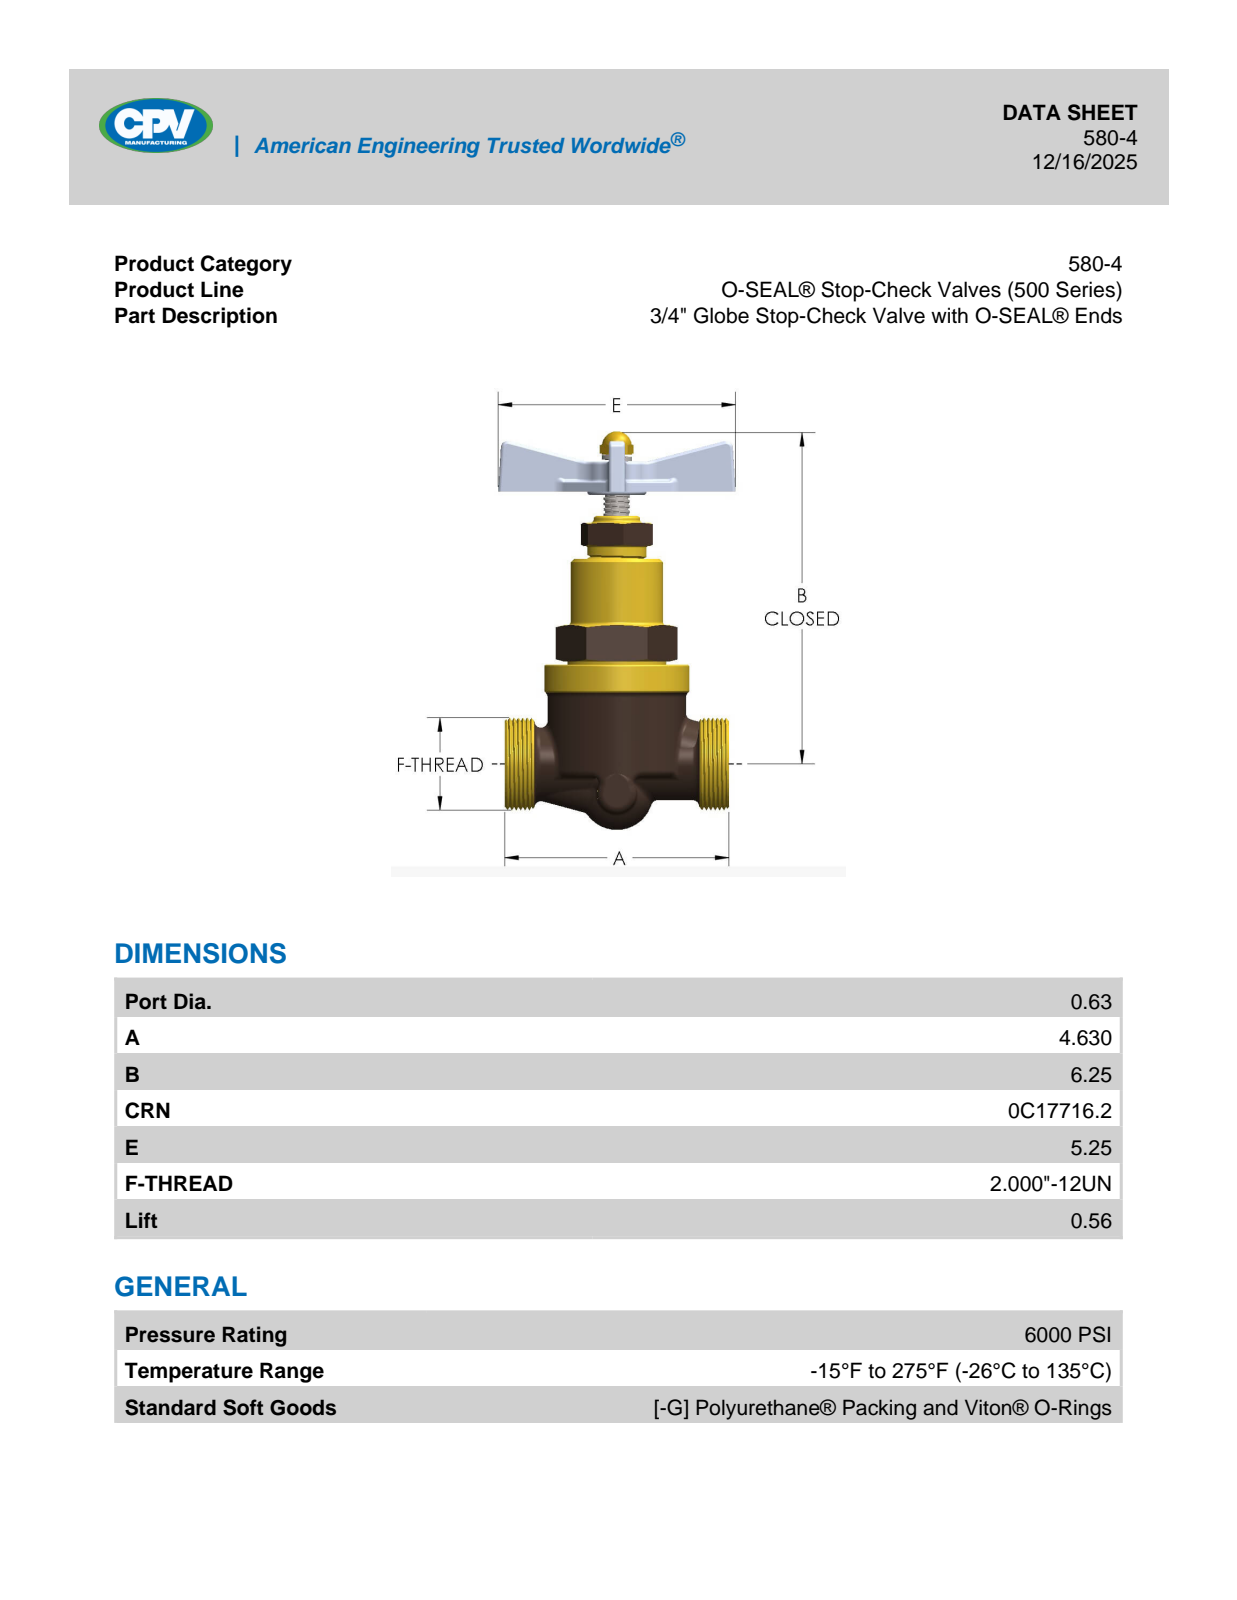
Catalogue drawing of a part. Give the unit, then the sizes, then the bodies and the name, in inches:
Units: inches
Overall size (bounding box): 7.676 × 5.25 × 5.25
Round holes (diameter × count): ⌀0.625 ×3, ⌀0.319 ×1, ⌀1.035 ×1, ⌀1.497 ×1, ⌀1.875 ×1, ⌀2 ×1
Round bosses / shafts (diameter × count): ⌀1.75 ×2, ⌀1 ×2, ⌀3 ×1, ⌀2.875 ×1, ⌀2 ×1, ⌀1.998 ×1, ⌀1.76 ×1, ⌀1.625 ×1
Partial cylindrical surfaces — rounded edges, fillets, slot ends (radius × count): R0.06 ×28, R0.13 ×16, R0.56 ×8, R0.03 ×4, R0.625 ×2, R0.125 ×1, R0.237 ×1, R0.325 ×1
Main face-to-face distances: 0.38, 2, 1.25, 1.75, 4.625, 1.885, 2.508, 2.117, 2.128, 2.497
Hole centre spacings: 1.582
Volume: 32.66 in³ · Surface area: 139.7 in²
Bodies: 2 solids, 737 faces (139 planar, 249 cylindrical, 349 other)
Part name (STEP PRODUCT): 380-4
STEP written by: SolidWorks 2018 (AUTOMOTIVE_DESIGN)
